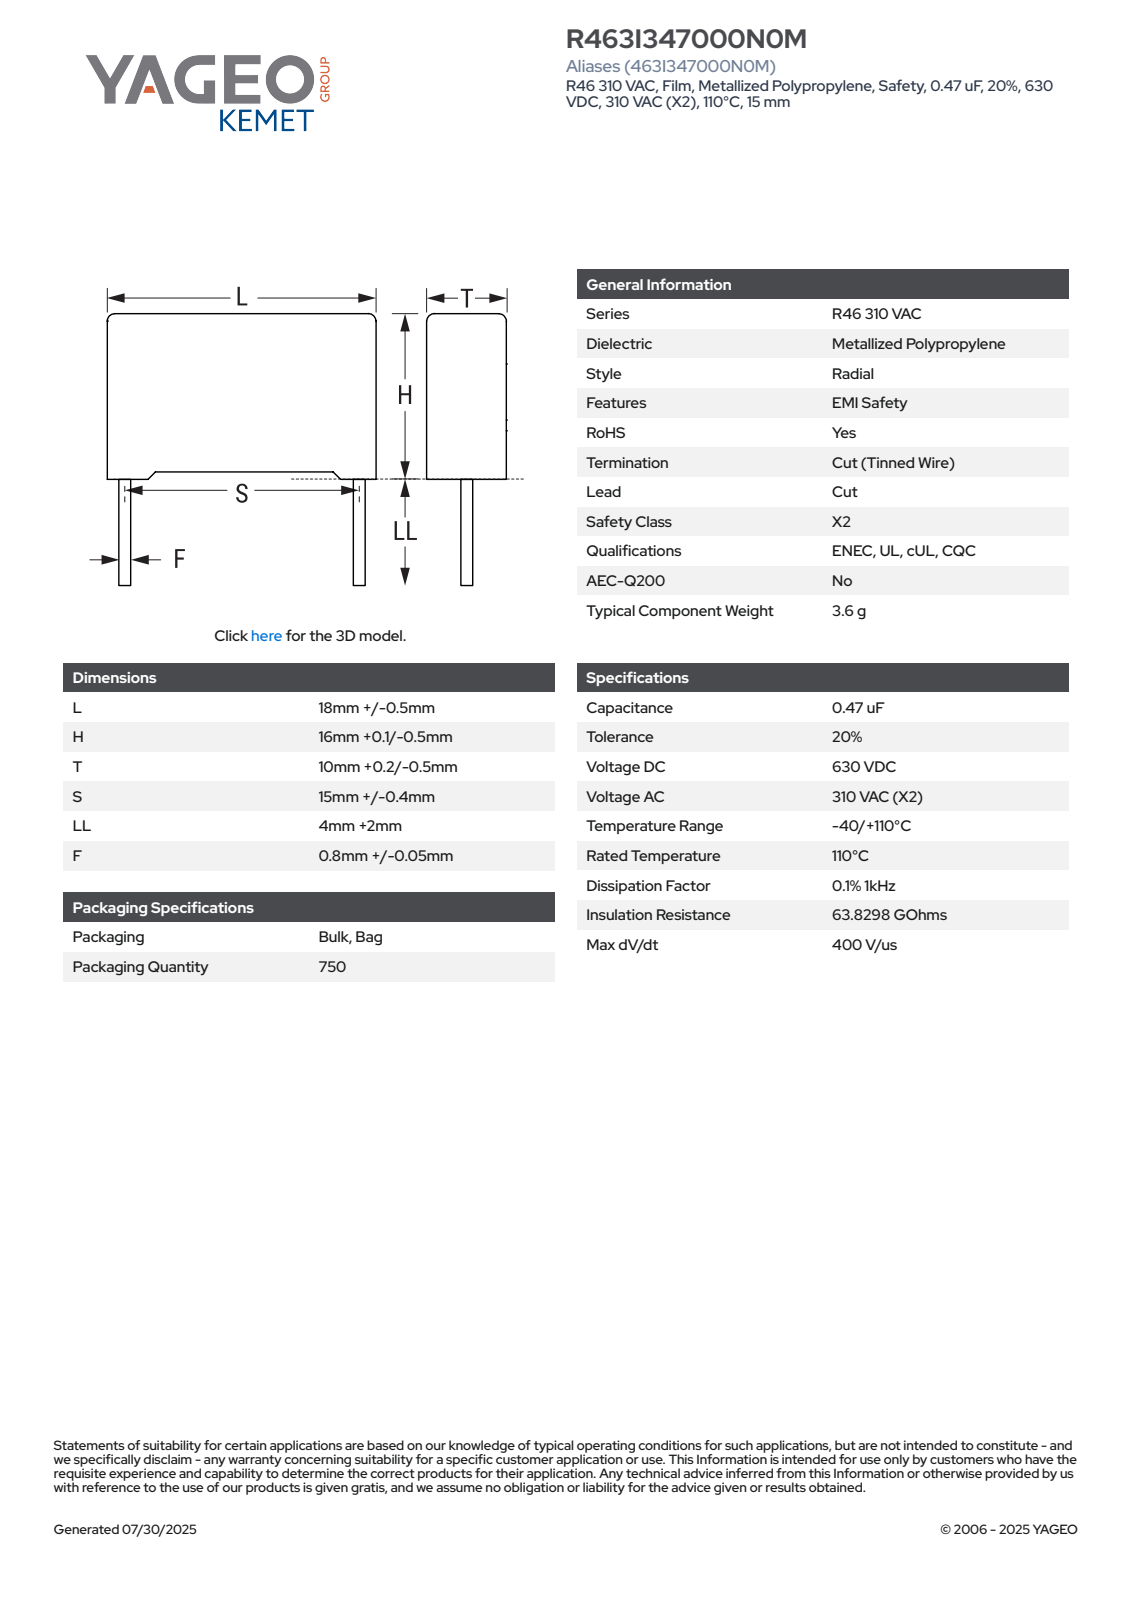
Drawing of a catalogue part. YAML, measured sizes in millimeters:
part_name: "CFR_RB2_18X16X10_L18.5H16.1T10.2S15LL6F0.85"
step_written_by: "SolidWorks 2021 (AUTOMOTIVE_DESIGN)"
units: millimeters
bodies: {solids: 4, faces: 85, planar: 77, cylindrical: 8, other: 0}
overall_size: [22.1, 18.5, 10.21]
volume: 2919
surface_area: 1365
round_bosses_or_shafts:
  - {diameter: 0.85, count: 2}
partial_cylinders:
  - {radius: 0.5, count: 4}
face_to_face_distances: [10.2, 18.5, 15.35, 0.62, 0.75, 16.1, 0.56, 15.54, 17.88, 9.58]
